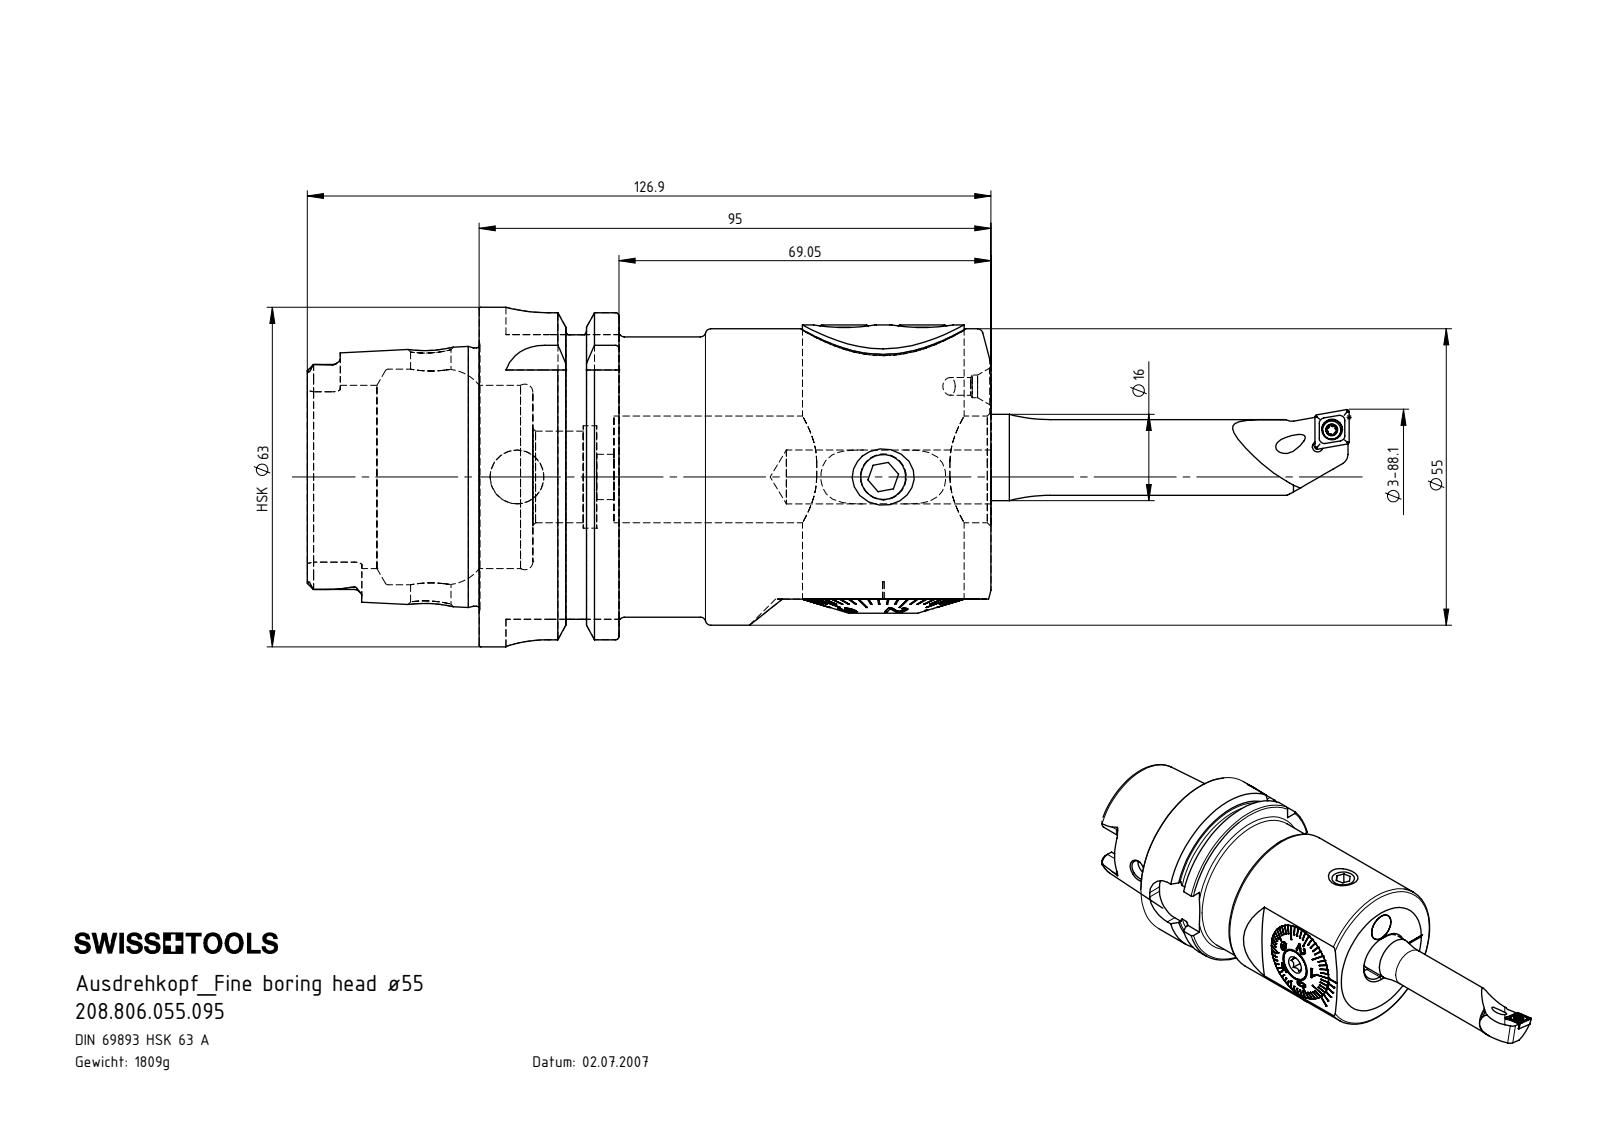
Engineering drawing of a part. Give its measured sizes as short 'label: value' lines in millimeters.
name: A55-BG1.014.041_Ausdrehbereich bis 1mm; ISO 4026 - M10 x 8; A55-BG2.015.007_B; HA6-A55.K00.095_B_Fertigbearbeitung (+8 more)
written by: SolidWorks 2017 (CONFIG_CONTROL_DESIGN)
unit: mm
bodies: 17 solids, 947 faces (374 planar, 201 cylindrical, 372 other)
size: 193.39 × 63 × 63
volume: 230 685 mm³; area: 62 302 mm²
holes: 3× ⌀8.5, 2× ⌀2, 2× ⌀3, 2× ⌀10, 1× ⌀1, 1× ⌀1.6, 1× ⌀2.05, 1× ⌀2.8, 1× ⌀3.3, 1× ⌀3.85, 1× ⌀4.2, 1× ⌀7.5
bosses: 3× ⌀10, 1× ⌀63, 1× ⌀55, 1× ⌀54.95, 1× ⌀52, 1× ⌀47.93, 1× ⌀30, 1× ⌀29.98
rounds: 6× R0.21, 6× R0.34, 6× R0.59, 6× R1.4, 5× R0.36, 4× R2.88, 4× R8, 3× R3.2
face distances: 95, 6.8, 16, 25.95, 69.05, 4, 2.8, 2.5, 9.95, 85.05
hole spacings: 7.25, 14.5, 3.63, 4.05, 4.15, 14.95, 15.67, 18.83
